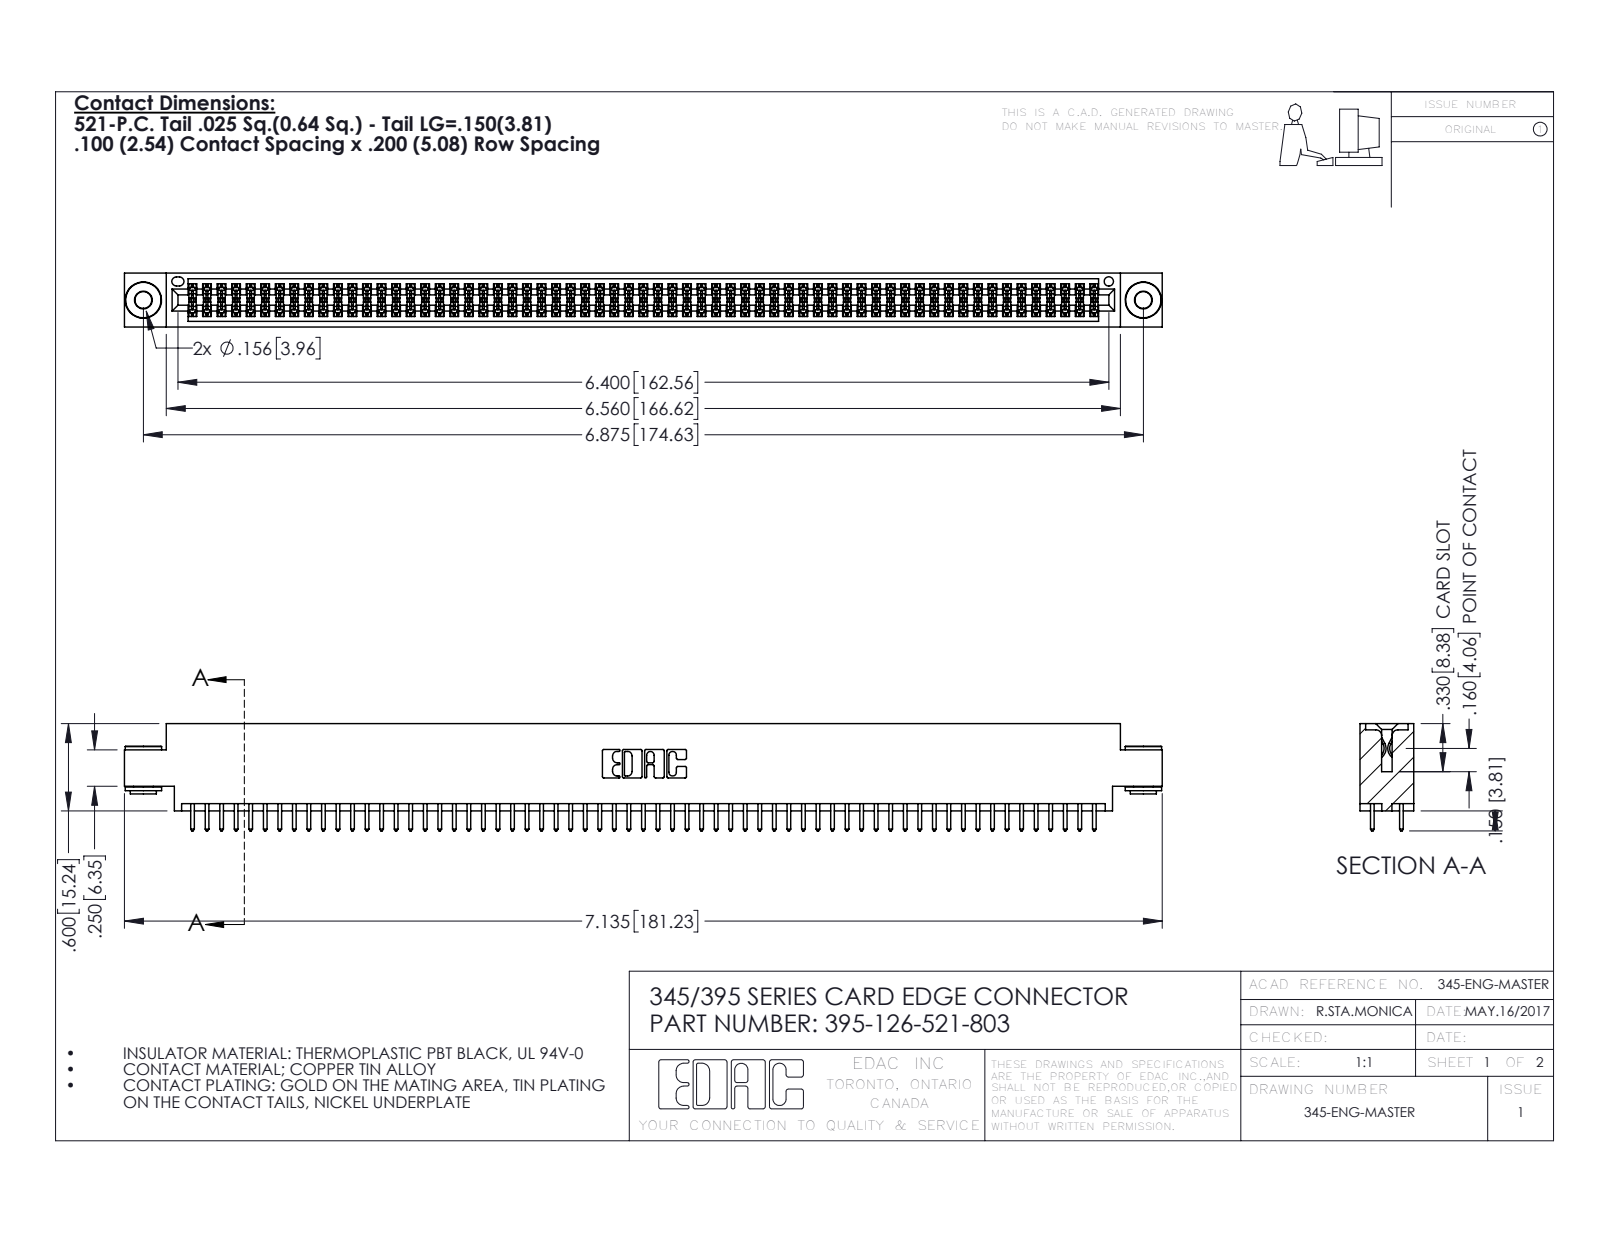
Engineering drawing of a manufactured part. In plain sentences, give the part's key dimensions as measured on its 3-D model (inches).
The part is named "345-292-001_345-293-121; 345-250-002_345-250-002-102; 345 Part_0.170 Offset - 0.156 Dia-TH; 395-126-521-803". Its 3-D file was written by "SolidWorks 2016 (CONFIG_CONTROL_DESIGN)". It is 129 solids with 6468 faces: 4252 planar, 2208 cylindrical and 8 other. Overall it measures 7.135 by 0.737 by 0.37 inches. Its volume is 1.077 cubic inches and its surface area 41.1 square inches. Round holes: 2 of diameter 0.116, 2 of diameter 0.156, 1 of diameter 0.064. Round bosses or shafts: 2 of diameter 0.25, 2 of diameter 0.18, 2 of diameter 0.136. Partial cylindrical surfaces (rounded edges, fillets, slot ends): 189 of radius 0.006, 126 of radius 0.01, 22 of radius 0.01, 6 of radius 0.007, 6 of radius 0.031, 3 of radius 0.026, 2 of radius 0.014, 2 of radius 0.019. The main face-to-face distances are 0.072, 0.298, 0.2, 0.37, 0.098, 0.272, 0.025, 0.225, 0.175, 0.149. The hole center spacings are 0.27, 6.639, 6.875.
